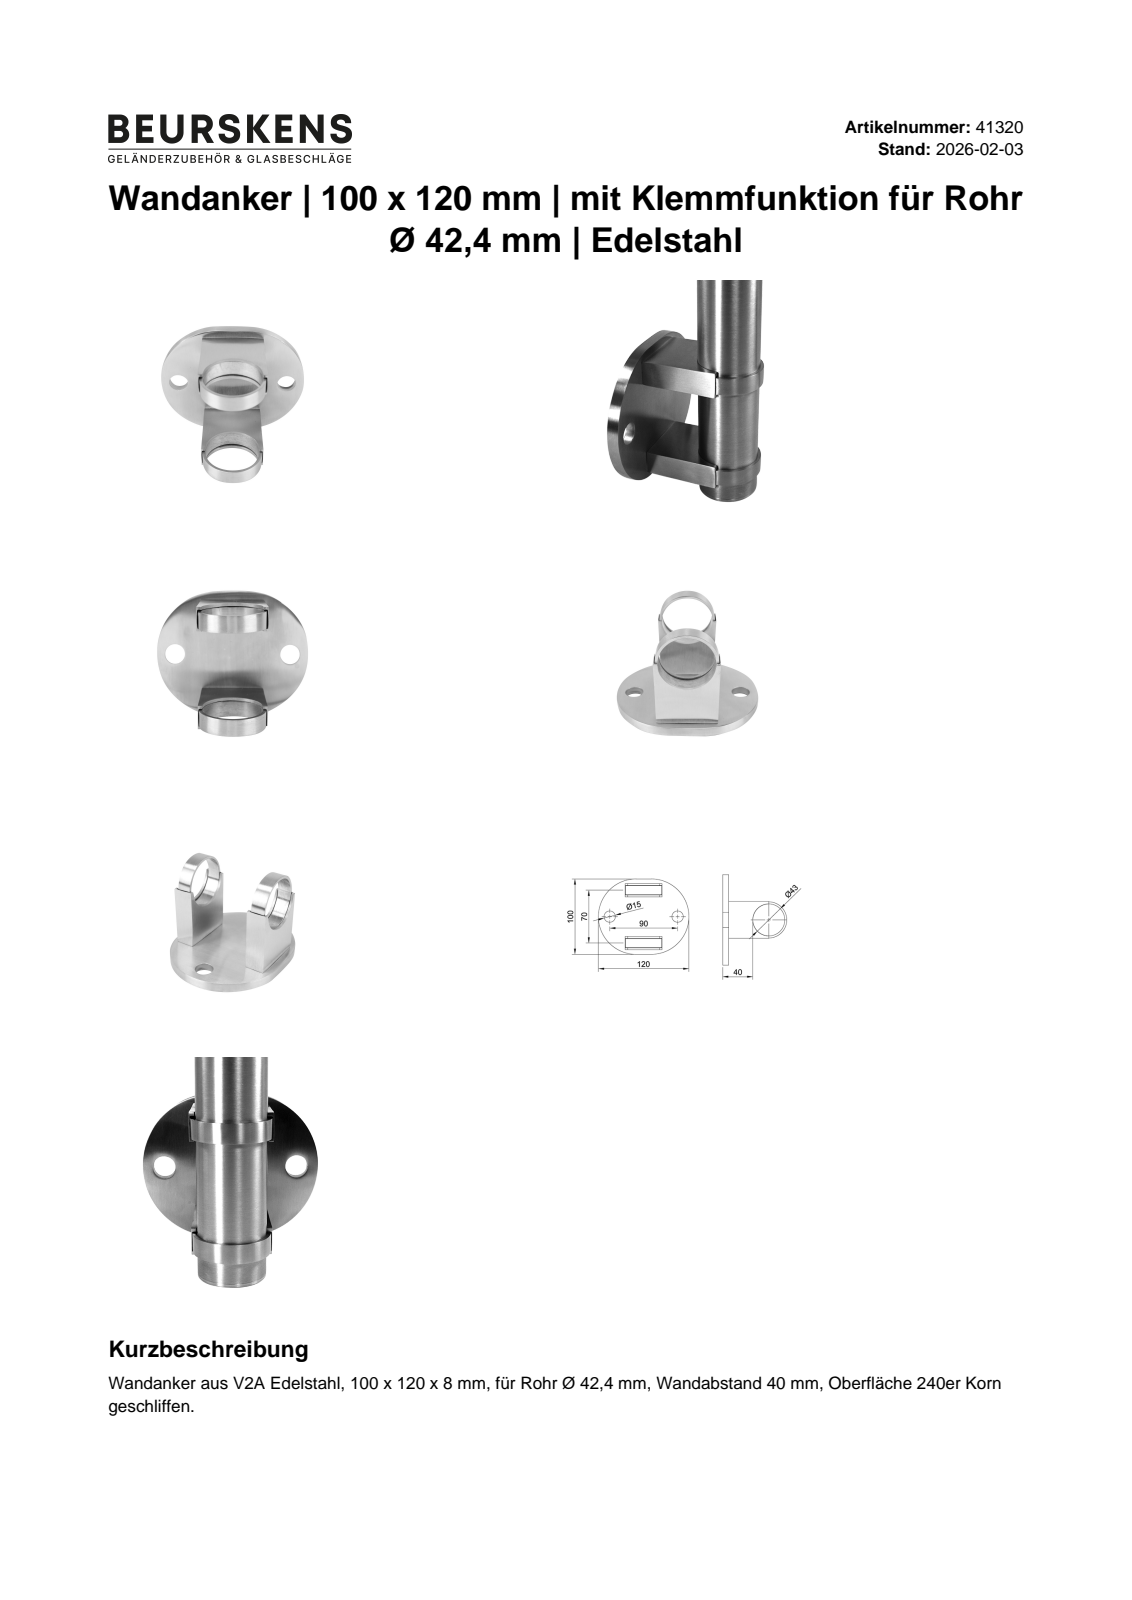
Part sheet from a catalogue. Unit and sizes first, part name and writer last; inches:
Units: inches
Overall size (bounding box): 4.724 × 3.937 × 3.346
Round holes (diameter × count): ⌀0.197 ×4, ⌀0.256 ×4, ⌀0.335 ×2, ⌀0.413 ×2, ⌀0.433 ×2, ⌀0.591 ×2, ⌀1.685 ×1
Round bosses / shafts (diameter × count): ⌀0.456 ×4, ⌀0.236 ×4, ⌀0.767 ×2, ⌀0.394 ×2
Partial cylindrical surfaces — rounded edges, fillets, slot ends (radius × count): R0.039 ×57, R0.207 ×4, R0.079 ×2, R0.118 ×2, R1.969 ×2, R0.835 ×1, R0.945 ×1, R0.955 ×1
Main face-to-face distances: 0.315, 2.756, 0.098, 0.591, 0.689, 0.581, 0.108, 0.482, 2.854, 3.346
Hole centre spacings: 0.689, 1.752, 2.244, 2.82, 2.841, 2.756, 1.378, 3.081
Volume: 7.91 in³ · Surface area: 98.25 in²
Bodies: 11 solids, 458 faces (154 planar, 172 cylindrical, 132 other)
Part name (STEP PRODUCT): 41320 for customer; socket countersunk head screw_din_DIN 7991 - M10 x 30 --- 20N; socket countersunk head screw_din_DIN 7991 - M6 x 16 --- 16N
STEP written by: SolidWorks 2020 (CONFIG_CONTROL_DESIGN)
